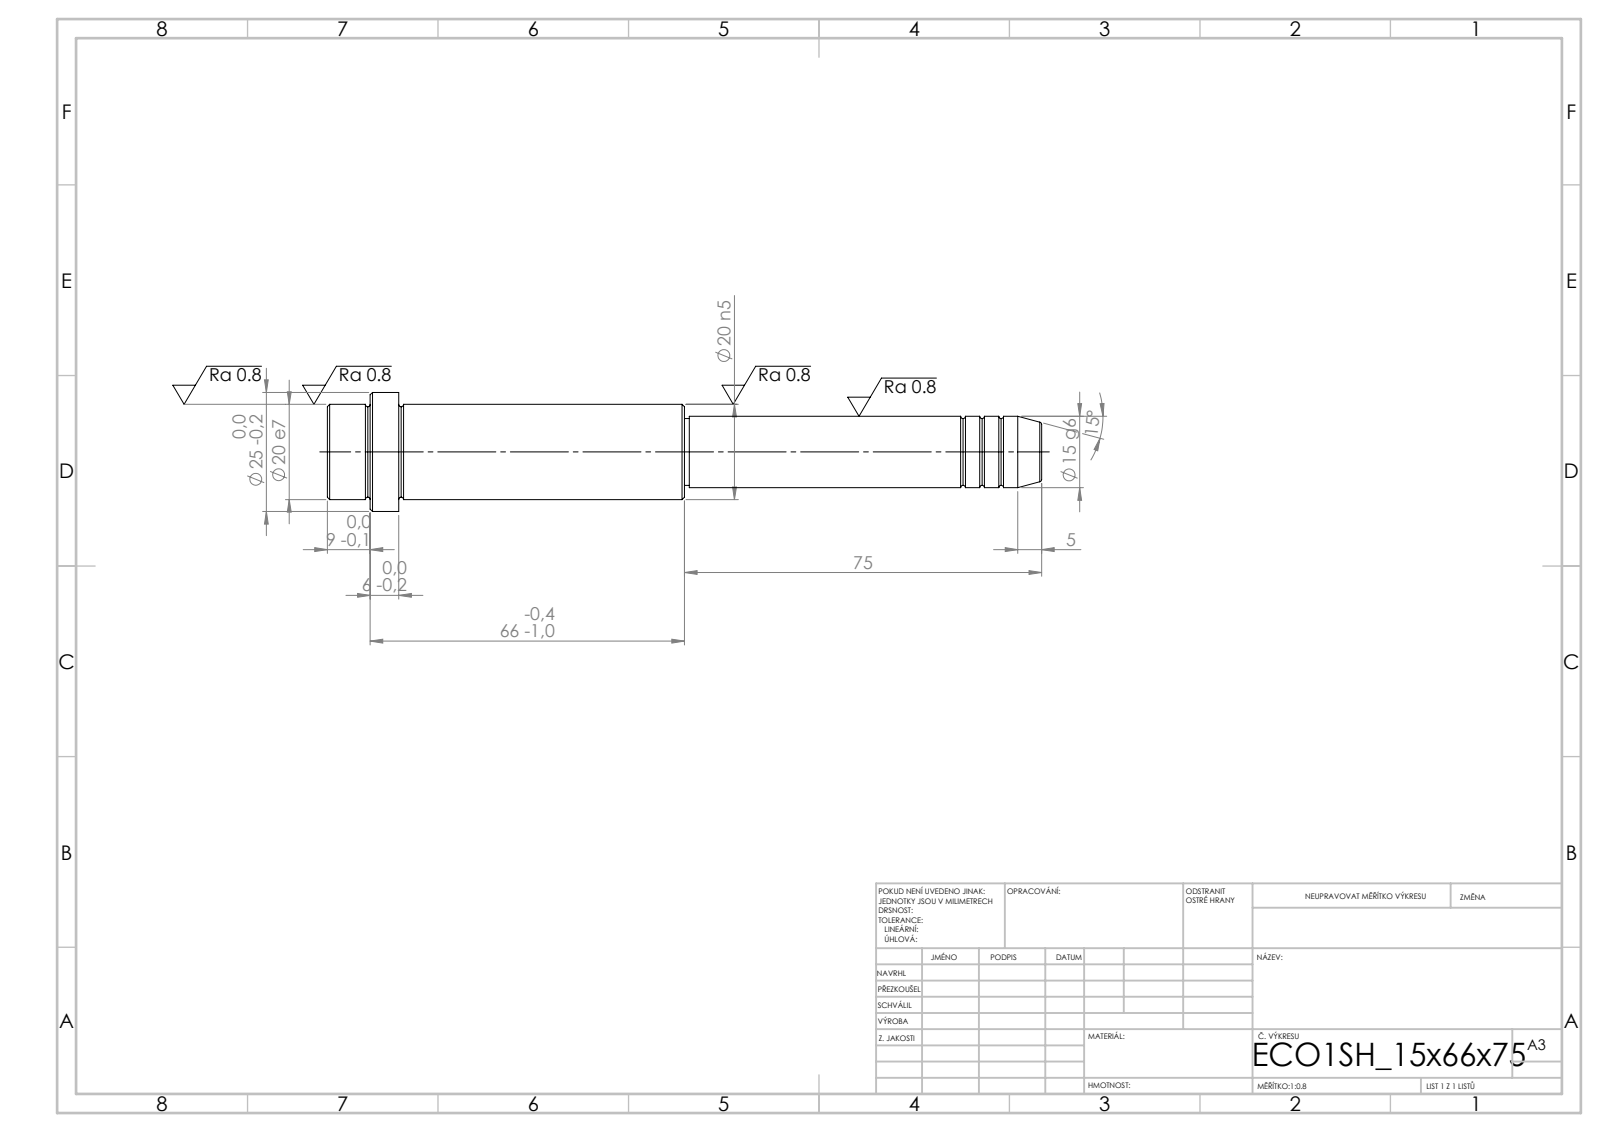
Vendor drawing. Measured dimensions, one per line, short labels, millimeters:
written by: SolidWorks 2019 (CONFIG_CONTROL_DESIGN)
unit: mm
bodies: 1 solid, 52 faces (6 planar, 16 cylindrical, 30 other)
size: 150 × 25 × 25
volume: 37 576 mm³; area: 9 366 mm²
bosses: 1× ⌀25, 1× ⌀20, 1× ⌀15, 1× ⌀14
face distances: 75, 15, 6, 9, 60, 66, 135, 141, 150, 74
